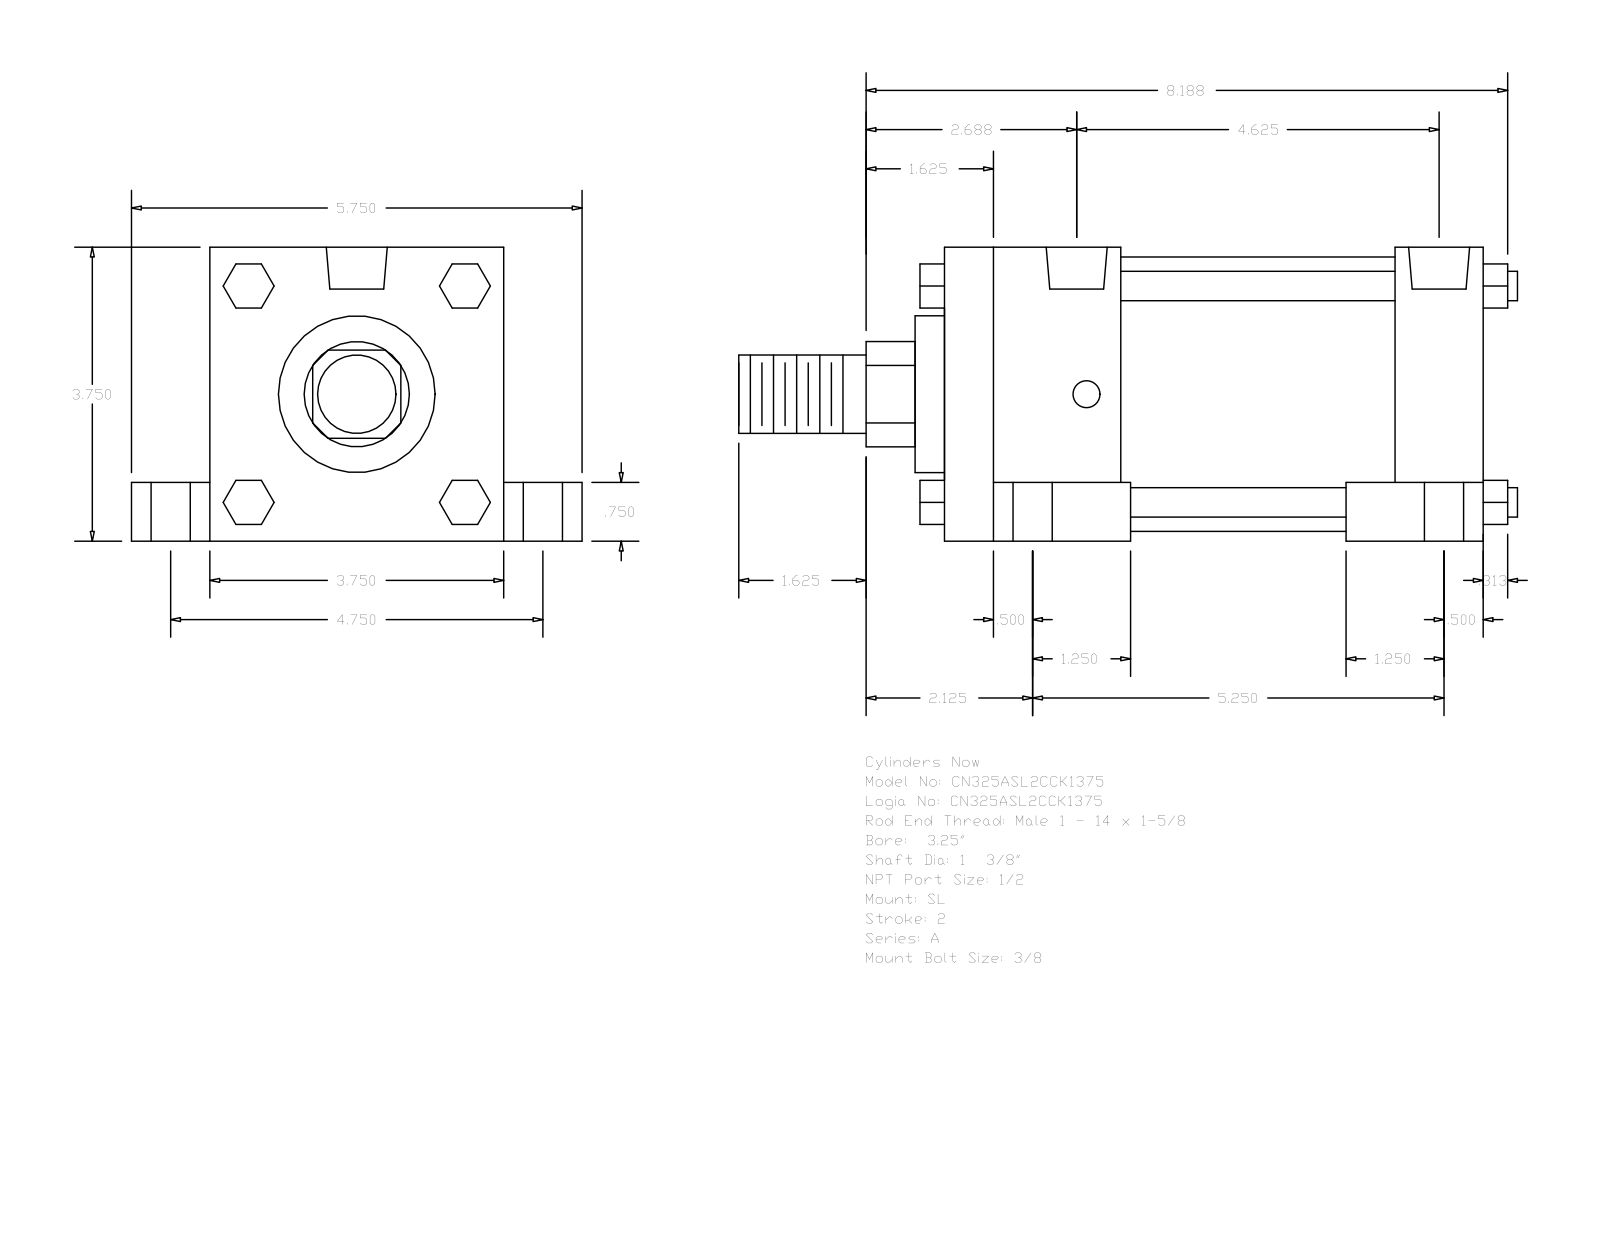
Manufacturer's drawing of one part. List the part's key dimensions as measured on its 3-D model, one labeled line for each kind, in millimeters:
Part name (STEP PRODUCT): A_SL__0325_1.375
STEP written by: GSSL Pune (CONFIG_CONTROL_DESIGN)
Units: millimetres
Bodies: 0 solids, 150 faces (114 planar, 36 cylindrical, 0 other)
Overall size (bounding box): 252.41 × 146.05 × 95.25
Round holes (diameter × count): ⌀8.73 ×4, ⌀12.7 ×4, ⌀19.05 ×4, ⌀19.77 ×2
Round bosses / shafts (diameter × count): ⌀9.53 ×4, ⌀88.9 ×1, ⌀50.8 ×1, ⌀34.92 ×1, ⌀25.4 ×1
Partial cylindrical surfaces — rounded edges, fillets, slot ends (radius × count): R17.06 ×1
Main face-to-face distances: 95.24, 174.63, 25.41, 120.65, 19.05, 76.19, 57.15, 28.58, 146.05, 88.9
Hole centre spacings: 3.18, 60.35, 60.52, 62, 62.81, 111.12, 114.3, 120.66
